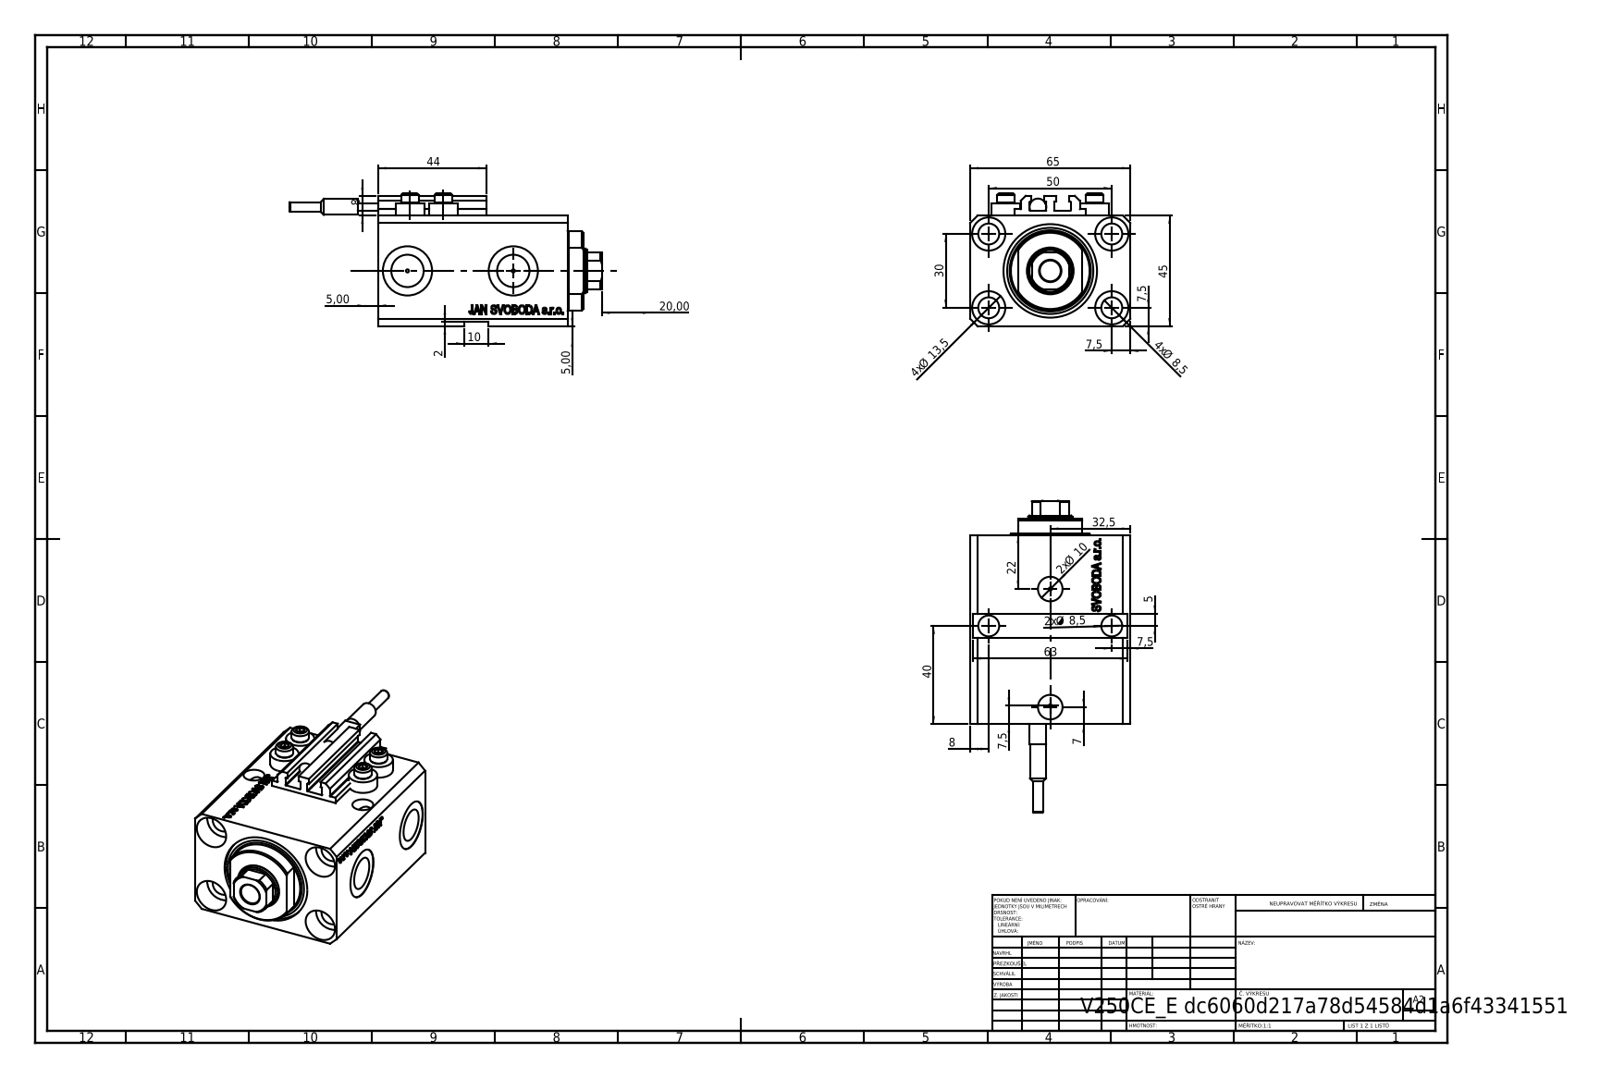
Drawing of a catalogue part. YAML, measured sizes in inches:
part_name: "V250CE_VC_E; SWITCH_V250CE; V250CE_E; ALLEN BOLT V250CE (+1 more)"
step_written_by: "SolidWorks 2019 (CONFIG_CONTROL_DESIGN)"
units: inches
bodies: {solids: 9, faces: 1109, planar: 531, cylindrical: 144, other: 434}
overall_size: [4.996, 2.559, 2.126]
volume: 12.08
surface_area: 98.85
round_holes:
  - {diameter: 0.335, count: 7}
  - {diameter: 0.049, count: 4}
  - {diameter: 0.157, count: 4}
  - {diameter: 0.531, count: 4}
  - {diameter: 0.394, count: 2}
  - {diameter: 0.518, count: 2}
  - {diameter: 0.787, count: 2}
  - {diameter: 0.709, count: 1}
  - {diameter: 0.984, count: 1}
  - {diameter: 1.496, count: 1}
round_bosses_or_shafts:
  - {diameter: 0.457, count: 4}
  - {diameter: 0.276, count: 4}
  - {diameter: 0.268, count: 1}
  - {diameter: 0.256, count: 1}
  - {diameter: 0.157, count: 1}
partial_cylinders:
  - {radius: 0.008, count: 10}
  - {radius: 0.335, count: 1}
  - {radius: 0.63, count: 1}
face_to_face_distances: [1.772, 2.559, 2.043, 0.988, 3.031, 0.079, 0.118, 0.272, 2.76, 1.85]
hole_center_spacings: [1.148, 1.969, 0.535, 0.595, 0.741, 0.747, 1.032, 1.048]
